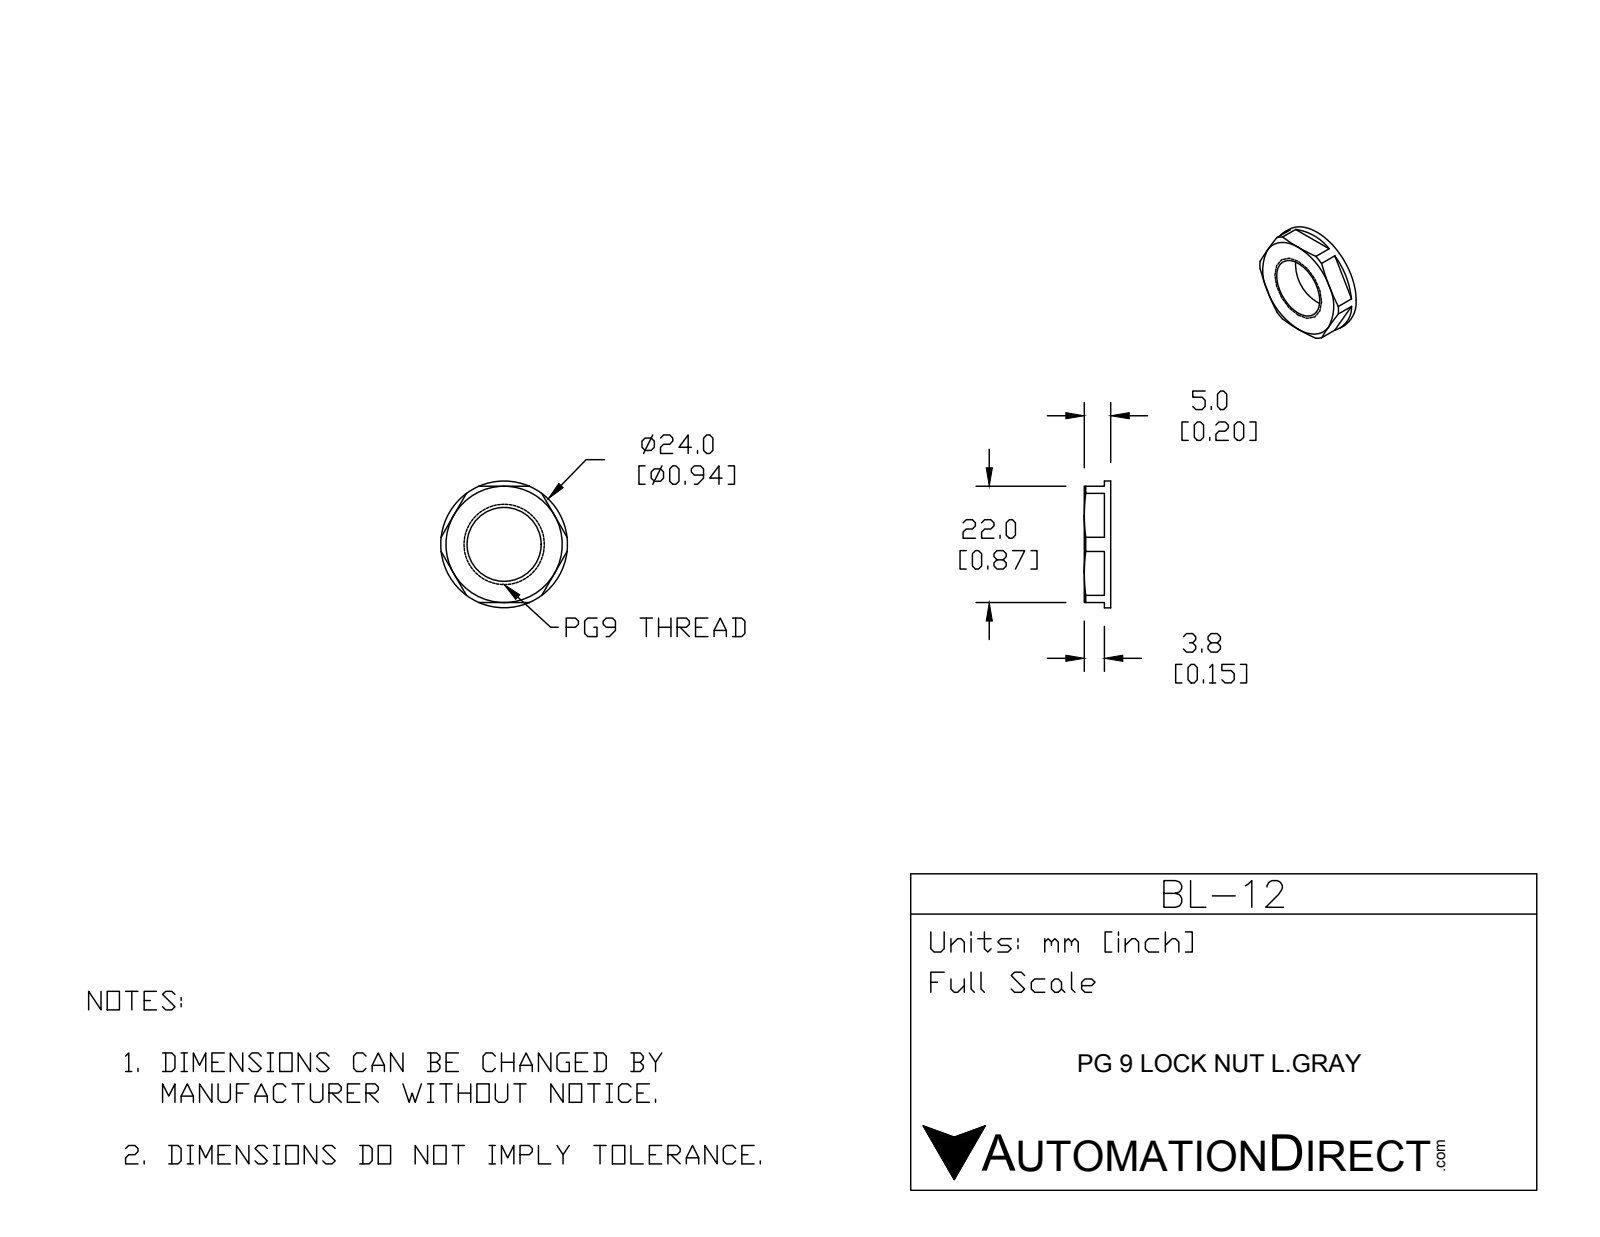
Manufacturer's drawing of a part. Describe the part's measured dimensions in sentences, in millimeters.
The part is named "BL-12". Its 3-D file was written by "SolidWorks 2015 (CONFIG_CONTROL_DESIGN)". It is 1 solid with 33 faces: 17 planar, 10 cylindrical and 6 other. Overall it measures 24 by 24 by 5 millimeters. Its volume is 1 340 cubic millimeters and its surface area 1 183 square millimeters. Round holes: 3 of diameter 1.5, 1 of diameter 14. Round bosses or shafts: 1 of diameter 24. The main face-to-face distances are 5, 22, 1.2, 3.8, 0.9, 4.7. The hole center spacings are 10.55, 18.28, 10.56, 18.27.
